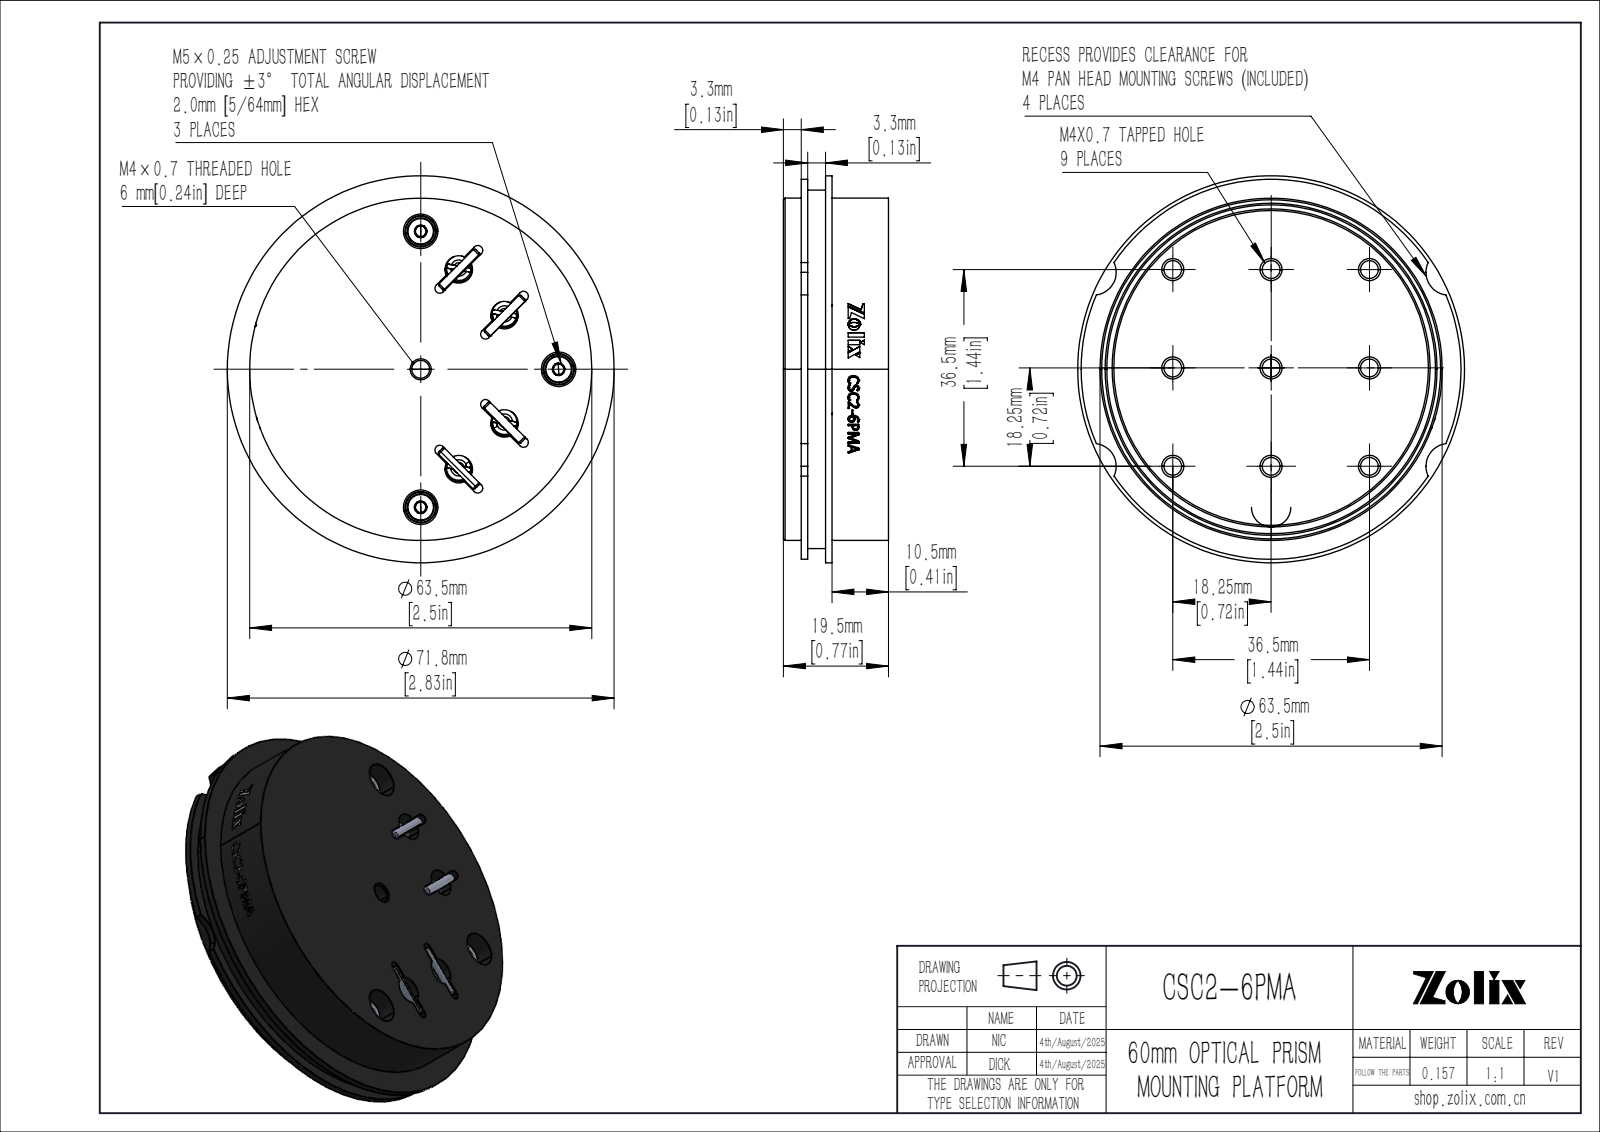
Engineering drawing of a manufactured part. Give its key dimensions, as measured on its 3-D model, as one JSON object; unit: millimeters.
{"part_name": "CSC2-6PMA", "step_written_by": "SolidWorks 2020 (CONFIG_CONTROL_DESIGN)", "units": "millimeters", "bodies": {"solids": 26, "faces": 853, "planar": 218, "cylindrical": 186, "other": 449}, "overall_size": [71.8, 71.8, 19.5], "volume_mm3": 58289, "surface_area_mm2": 26863, "round_holes": [[3.3, 10], [5.1, 8], [2.71, 4], [1.95, 3], [4, 3], [5, 3], [6.4, 3], [7.3, 3], [3, 1], [3.5, 1], [6, 1], [61, 1]], "round_bosses_or_shafts": [[3.48, 4], [1.6, 4], [7.1, 3], [6, 3], [1.5, 2], [71.8, 1], [70.5, 1], [66.5, 1]], "partial_cylinders_radius": [[0.9, 8], [4.25, 4], [0.75, 2], [0.69, 1], [31.73, 1]], "face_to_face_distances": [12.7, 19.5, 6.8, 1.3, 14, 5.5, 3.5, 2.2, 4.5, 3.3], "hole_center_spacings": [18.25, 25.81, 40.81, 25.6, 36.5, 19.83, 10, 12.01]}
